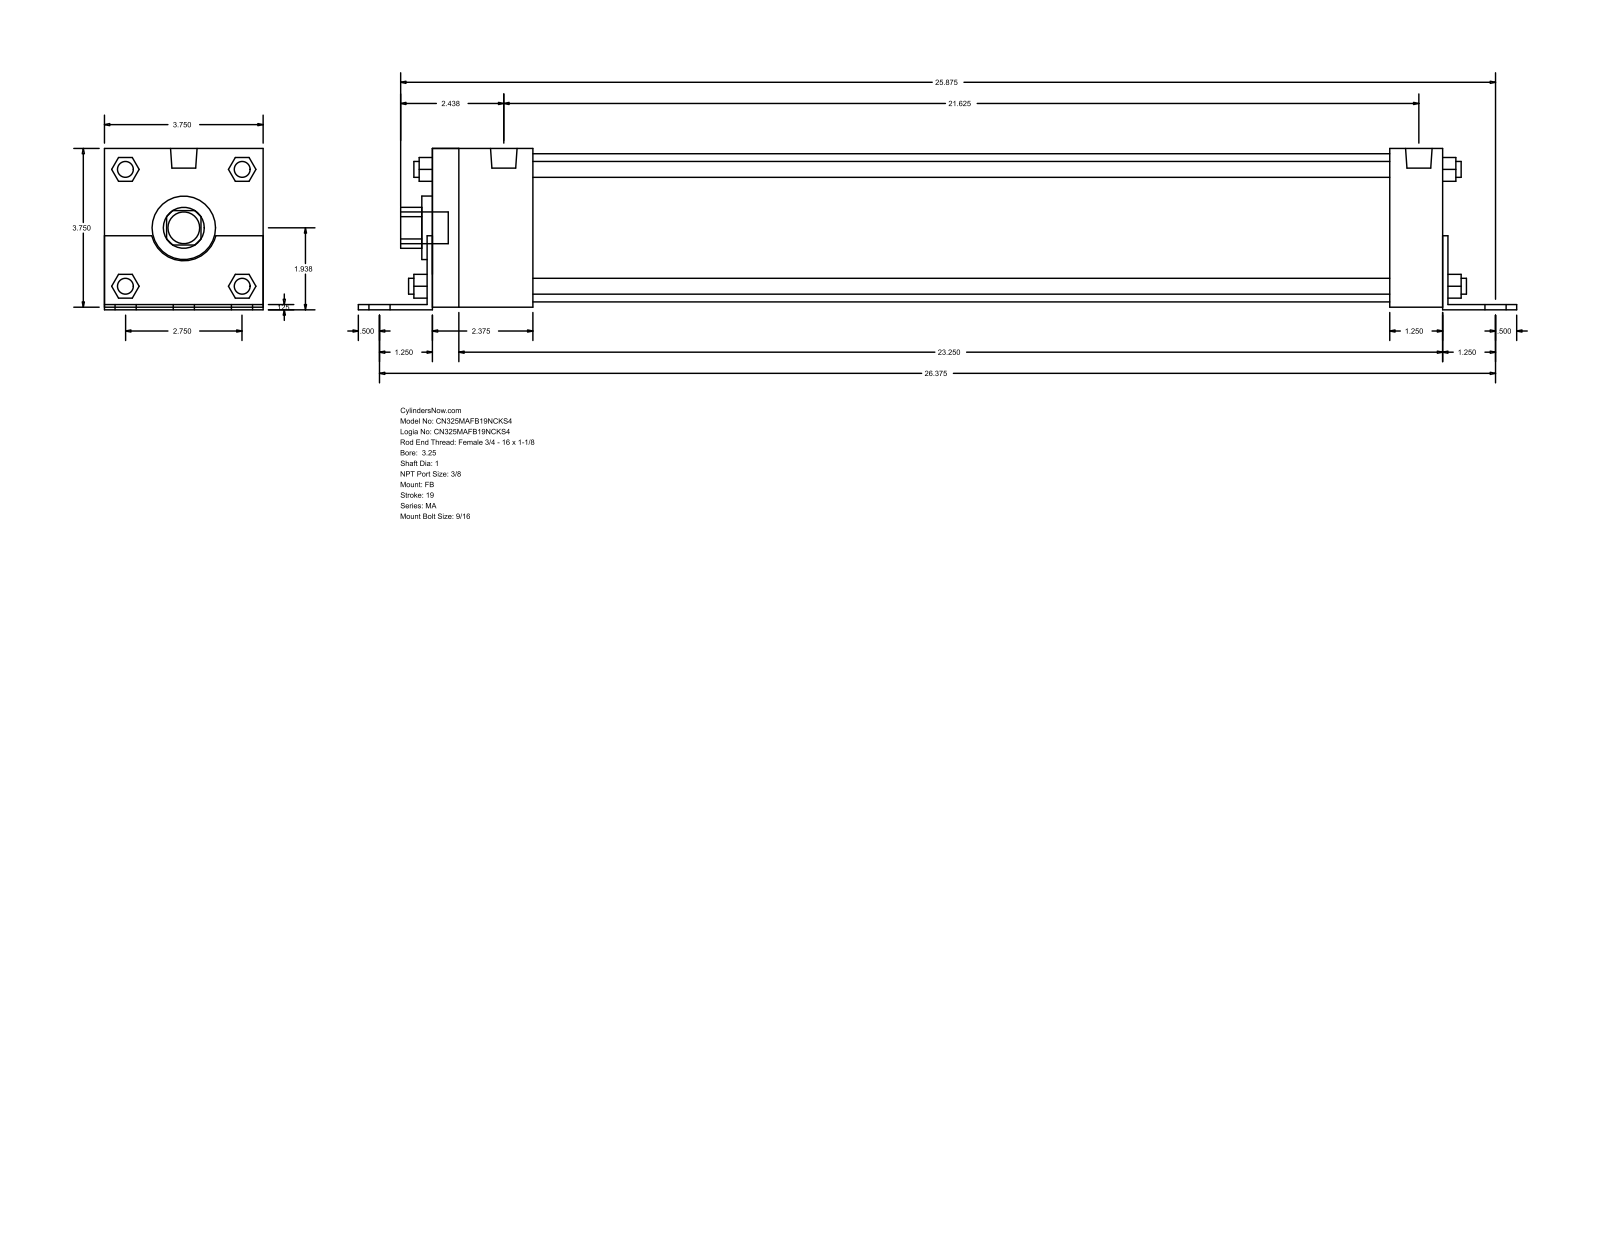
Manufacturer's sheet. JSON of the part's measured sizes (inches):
{"part_name": "MA_FB__0325_1", "step_written_by": "GSSL Pune (CONFIG_CONTROL_DESIGN)", "units": "inches", "bodies": {"solids": 0, "faces": 140, "planar": 105, "cylindrical": 35, "other": 0}, "overall_size": [27.375, 3.813, 3.75], "round_holes": [[1, 1], [1.5, 1], [3.5, 1]], "round_bosses_or_shafts": [[0.563, 6], [0.437, 4], [0.375, 4], [0.627, 2], [0.75, 1]], "partial_cylinders_radius": [[0.484, 1], [0.78, 1]], "face_to_face_distances": [3.75, 0.125, 0.063, 3.812, 0.062, 3.687, 24, 23.875, 24.125, 22.75]}
